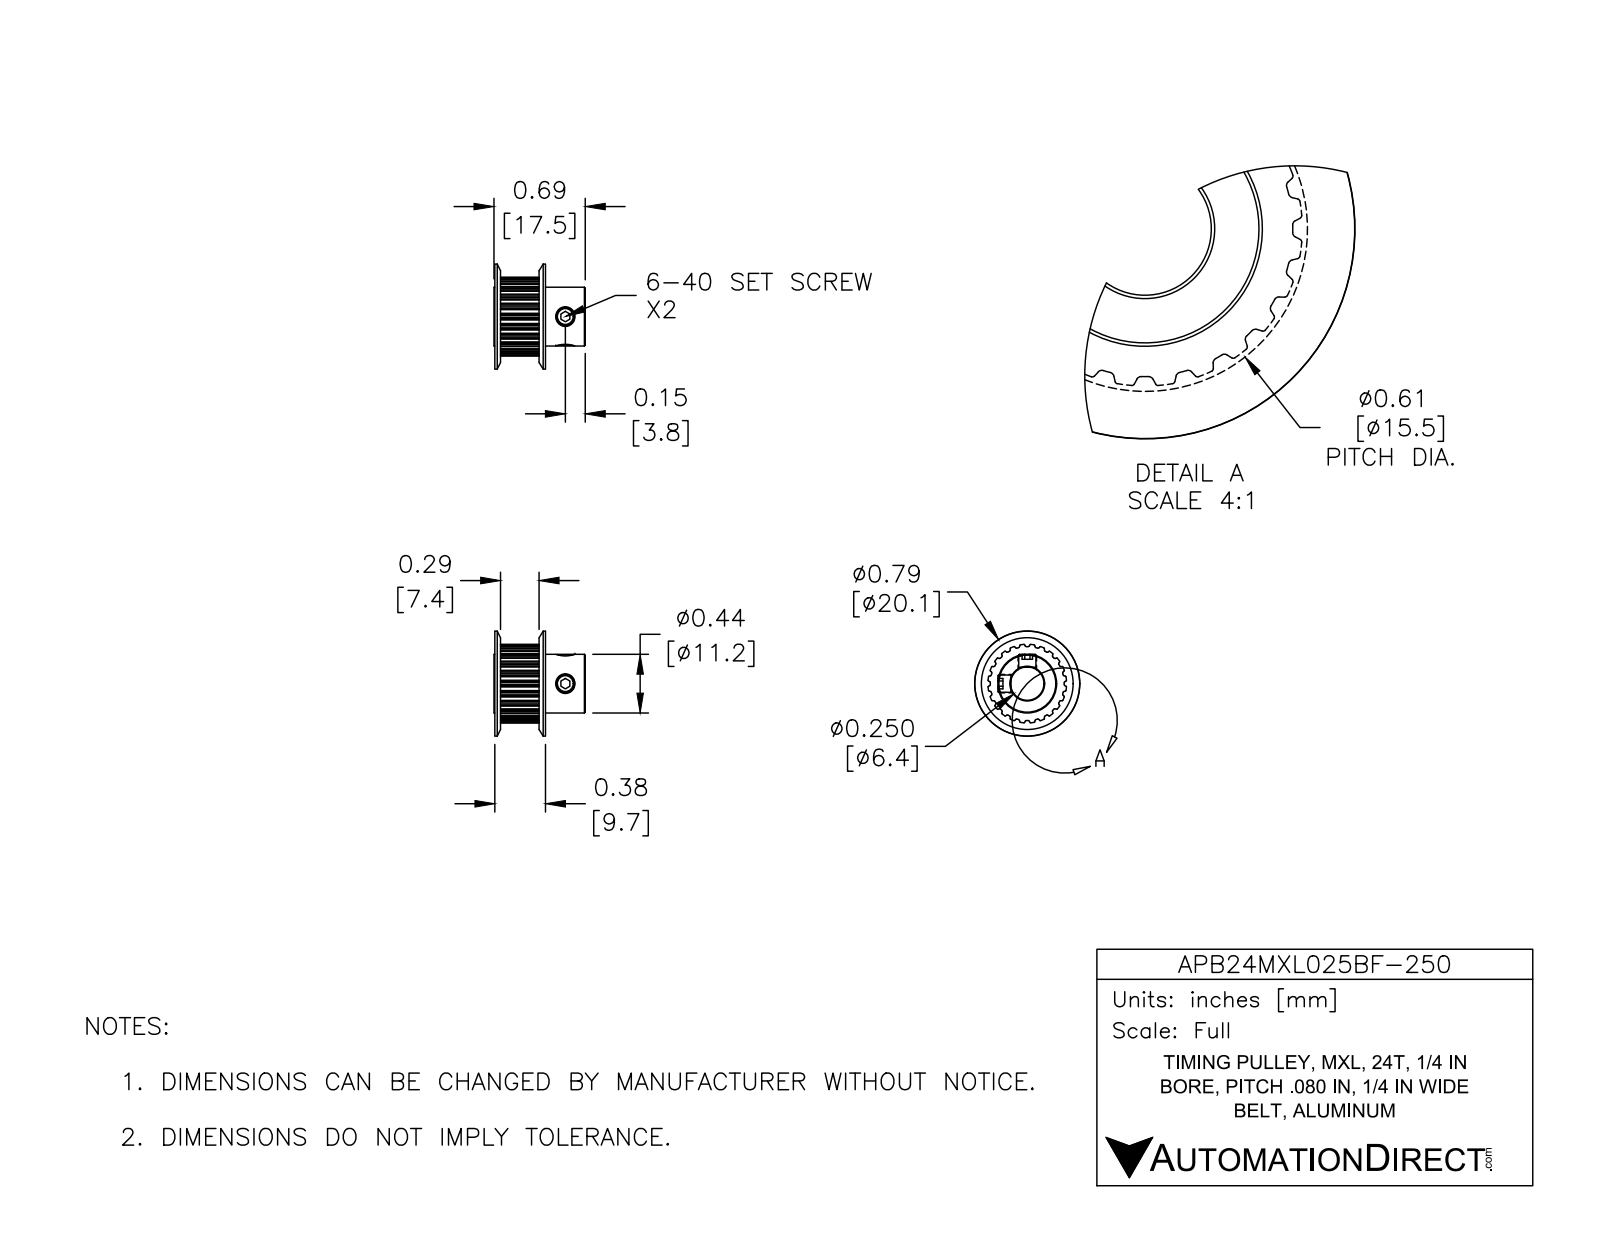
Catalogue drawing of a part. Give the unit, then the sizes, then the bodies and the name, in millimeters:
Units: millimetres
Overall size (bounding box): 20.1 × 20.1 × 17.5
Round holes (diameter × count): ⌀3.5 ×2, ⌀6.4 ×1
Round bosses / shafts (diameter × count): ⌀3.3 ×2, ⌀11.2 ×1
Partial cylindrical surfaces — rounded edges, fillets, slot ends (radius × count): R0.1 ×48, R0.2 ×48, R7.1 ×1, R7.5 ×1
Main face-to-face distances: 8.8, 0.6, 9.4, 17.4, 16.8, 8.1, 6.1, 1.3, 0.6, 8.1
Volume: 1 950 mm³ · Surface area: 2 121 mm²
Bodies: 3 solids, 277 faces (72 planar, 179 cylindrical, 26 other)
Part name (STEP PRODUCT): APB24MXL025BF-250
STEP written by: SolidWorks 2016 (AUTOMOTIVE_DESIGN)
